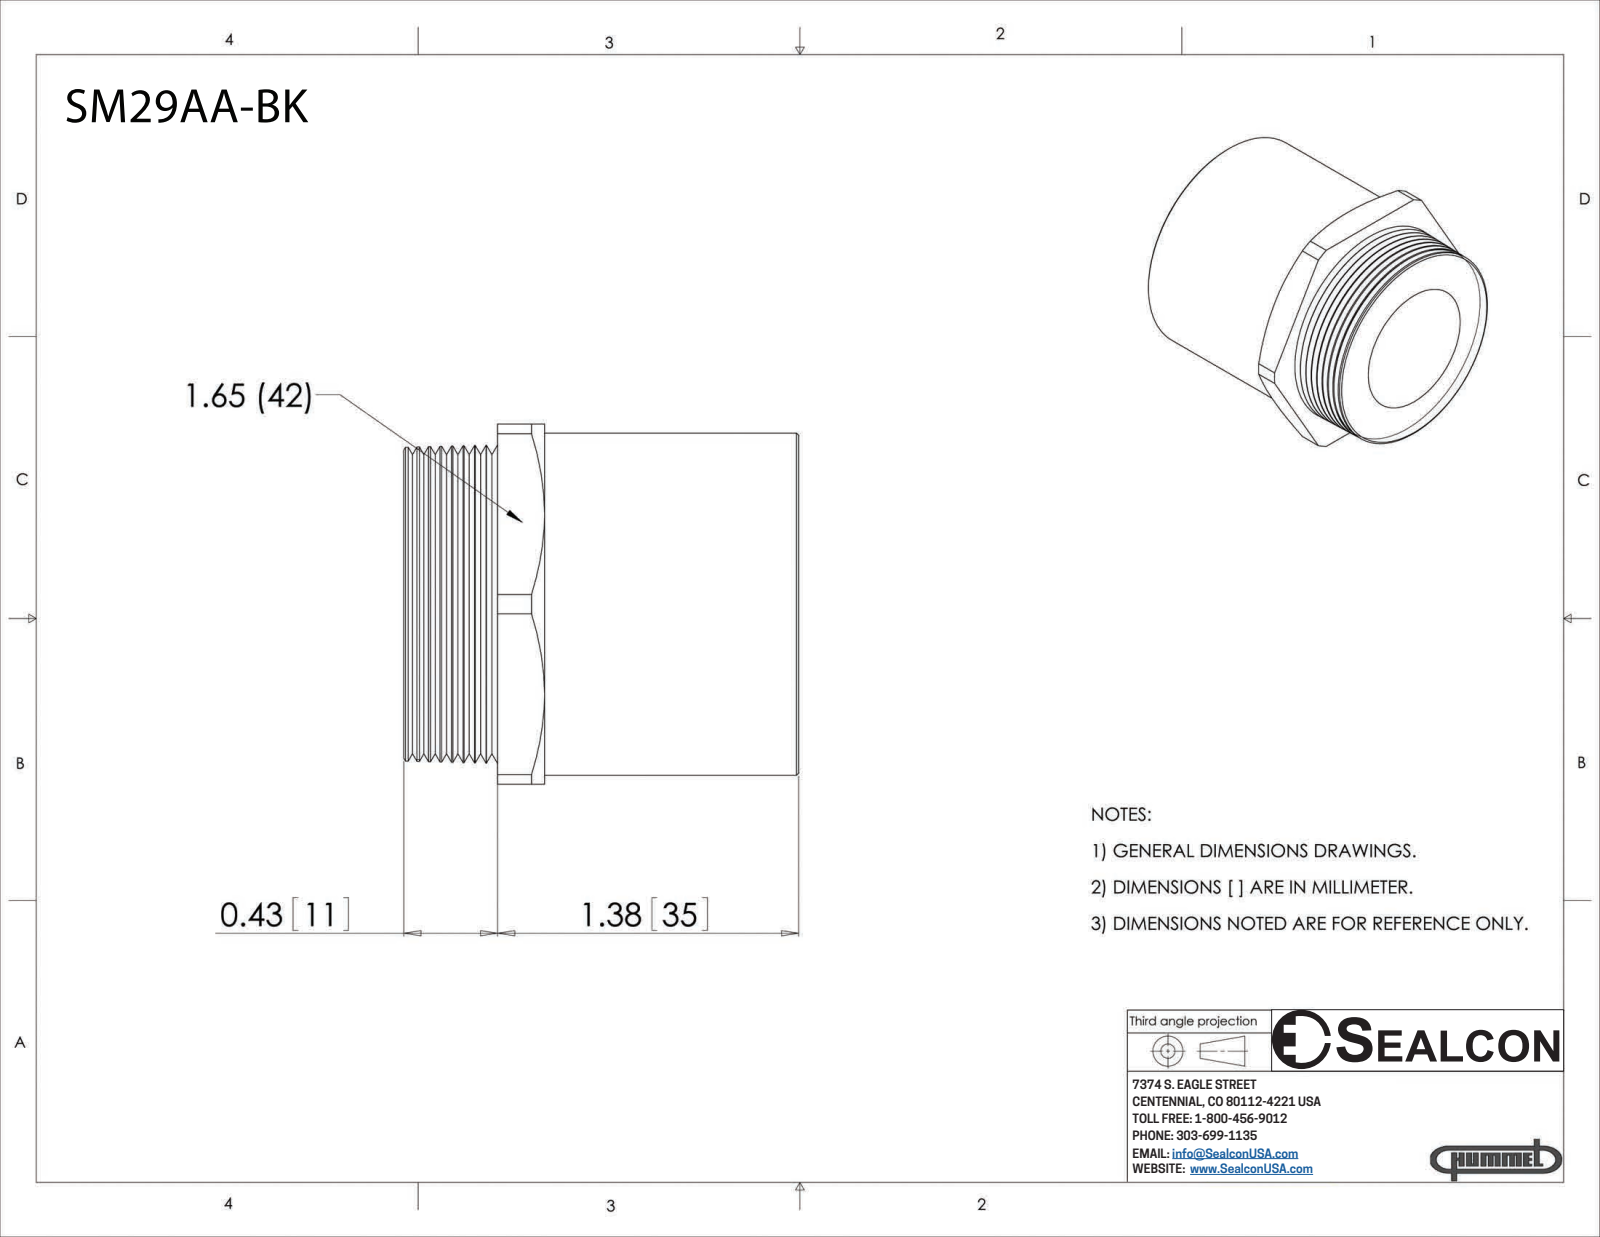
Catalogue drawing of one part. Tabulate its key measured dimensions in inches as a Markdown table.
| quantity | value |
| --- | --- |
| part name | SM29AA-BK |
| STEP written by | SolidWorks 2007 (AUTOMOTIVE_DESIGN) |
| units | inches |
| bodies | 1 solid, 83 faces (11 planar, 11 cylindrical, 61 other) |
| overall size | 1.856 × 1.81 × 1.65 |
| volume | 1.083 in³ |
| surface area | 20.95 in² |
| round holes (diameter × count) | 1.47 × 1 |
| round bosses / shafts (diameter × count) | 1.567 × 1 |
| partial cylindrical surfaces (radius × count) | 0.928 × 1 |
| main face-to-face distances | 0.645, 0.215, 0.43, 1.65, 1.165, 1.38, 1.81, 1.65 |
